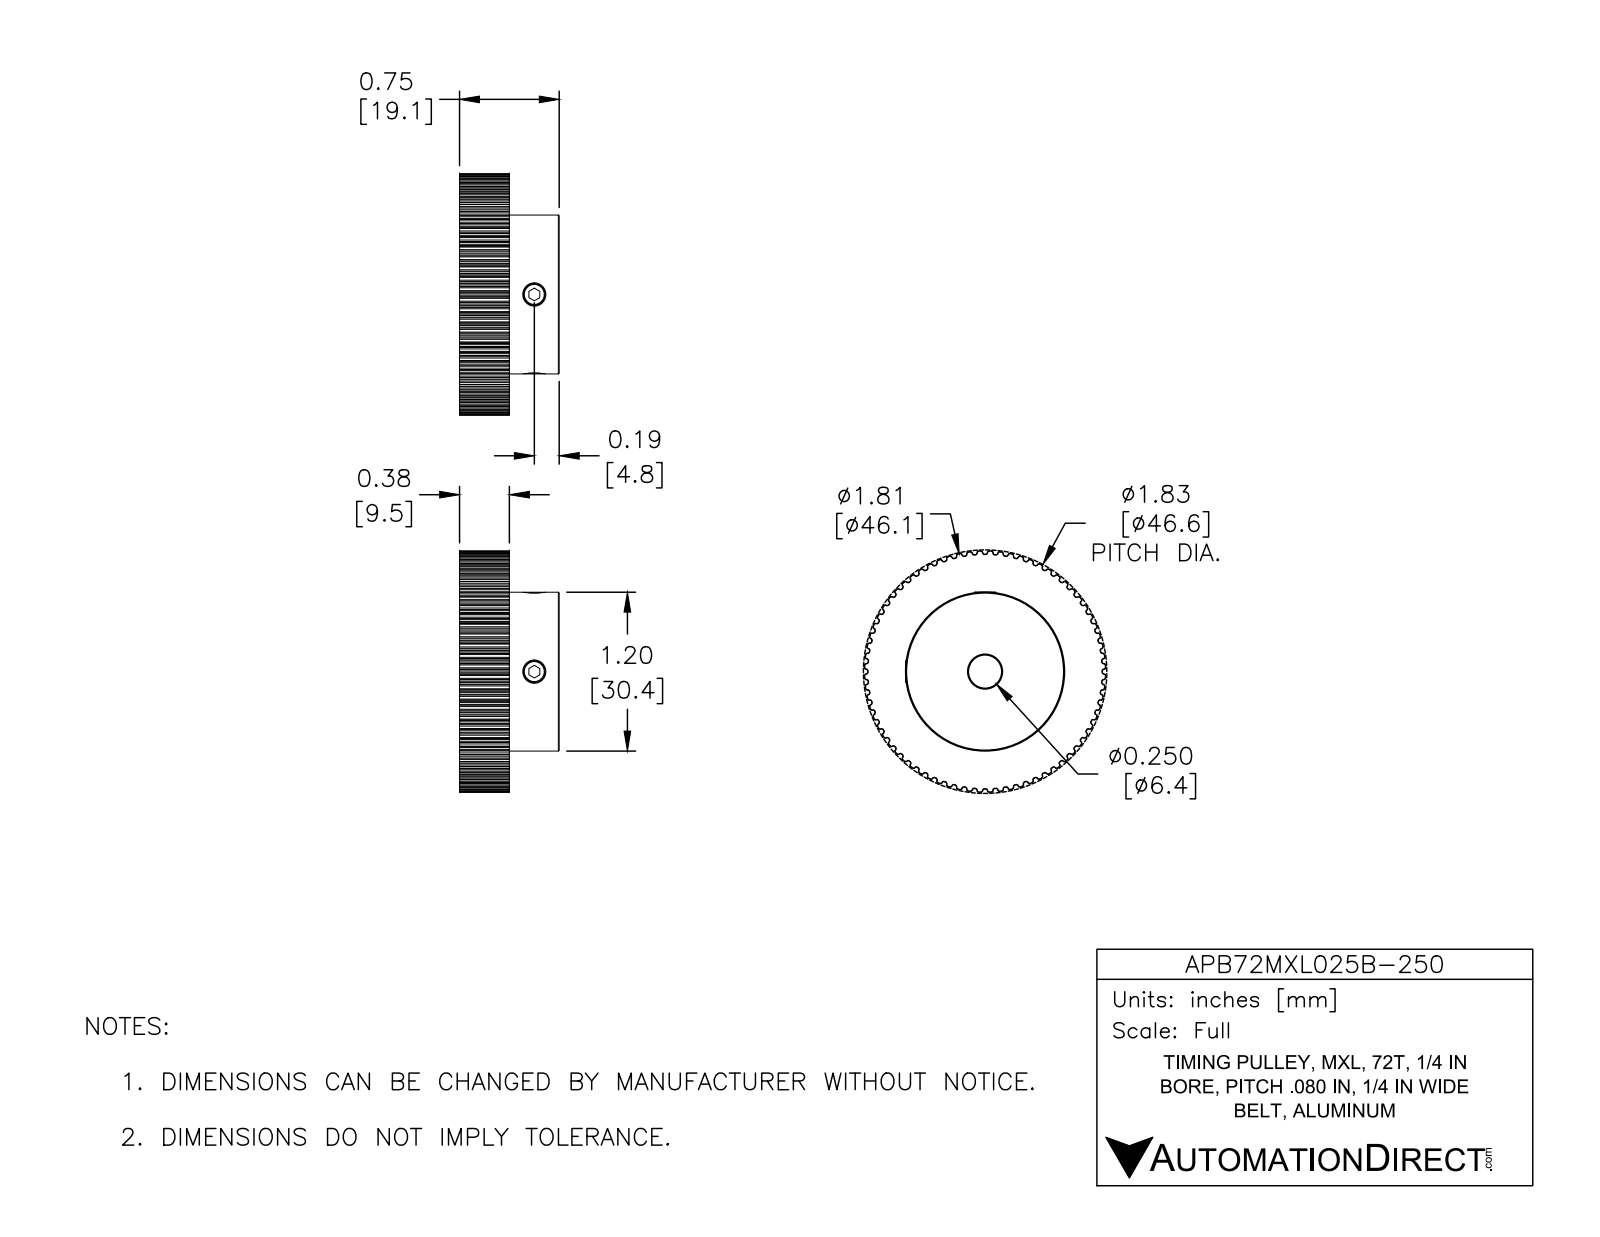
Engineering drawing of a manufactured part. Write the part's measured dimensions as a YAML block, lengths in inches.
part_name: "APB72MXL025B-250"
step_written_by: "SolidWorks 2016 (AUTOMOTIVE_DESIGN)"
units: inches
bodies: {solids: 3, faces: 677, planar: 237, cylindrical: 426, other: 14}
overall_size: [1.813, 1.813, 0.75]
volume: 1.312
surface_area: 10.39
round_holes:
  - {diameter: 0.164, count: 2}
  - {diameter: 0.25, count: 1}
round_bosses_or_shafts:
  - {diameter: 0.16, count: 2}
  - {diameter: 1.195, count: 1}
partial_cylinders:
  - {radius: 0.009, count: 144}
  - {radius: 0.012, count: 144}
  - {radius: 0.907, count: 1}
face_to_face_distances: [0.375, 0.75, 0.375, 0.578, 0.593, 1.171, 0.593, 1.171, 1.172, 1.765]
